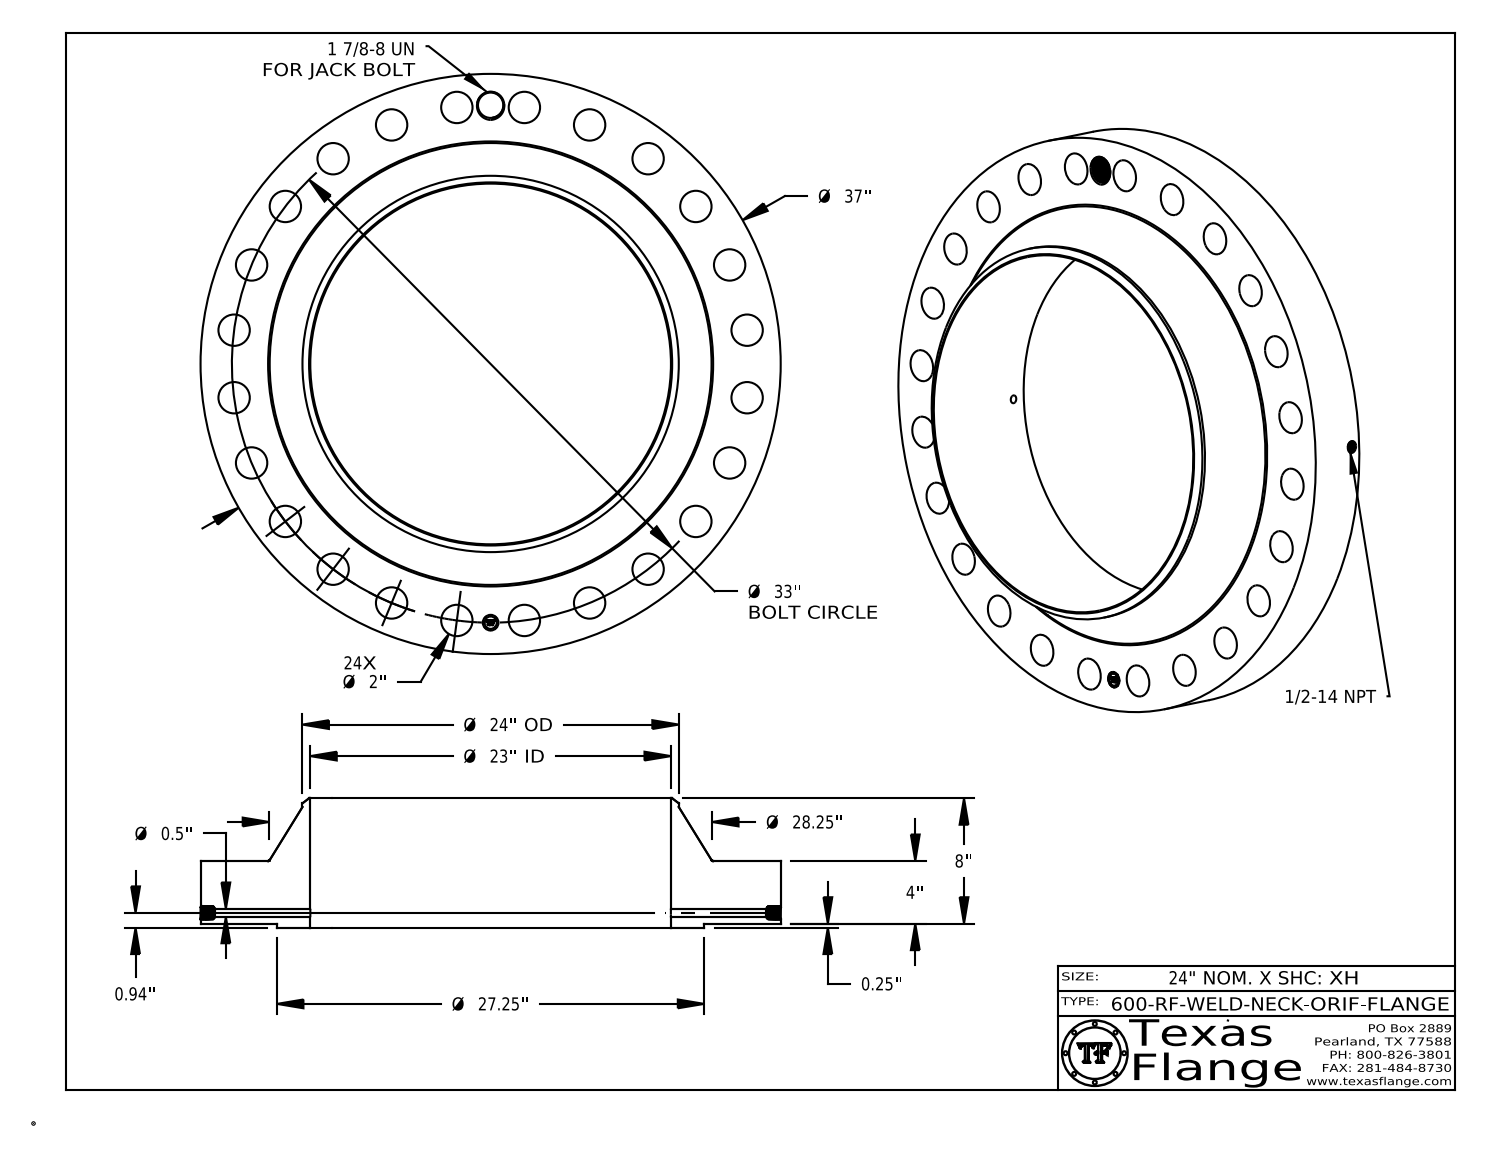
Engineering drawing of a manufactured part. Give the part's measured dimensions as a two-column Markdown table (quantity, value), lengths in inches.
| quantity | value |
| --- | --- |
| part name | 600-RF-WELD-NECK |
| STEP written by | CATIA V5 STEP AP214 (AUTOMOTIVE_DESIGN) |
| units | inches |
| bodies | 1 solid, 903 faces (369 planar, 159 cylindrical, 375 other) |
| overall size | 37 × 37 × 8.25 |
| volume | 2 801 in³ |
| surface area | 3 108 in² |
| round holes (diameter × count) | 2 × 24, 0.5 × 1, 0.672 × 1, 1 × 1, 1.615 × 1, 23 × 1 |
| round bosses / shafts (diameter × count) | 0.061 × 8, 37 × 1, 27.25 × 1, 24 × 1, 0.788 × 1 |
| main face-to-face distances | 4, 0.25, 4.25, 8.25, 8, 4.235, 3.985, 0.015, 4.015, 0.298 |
| hole center spacings | 16.5, 8.541, 20.089, 28.579, 12.628, 4.307, 23.334, 26.181 |
